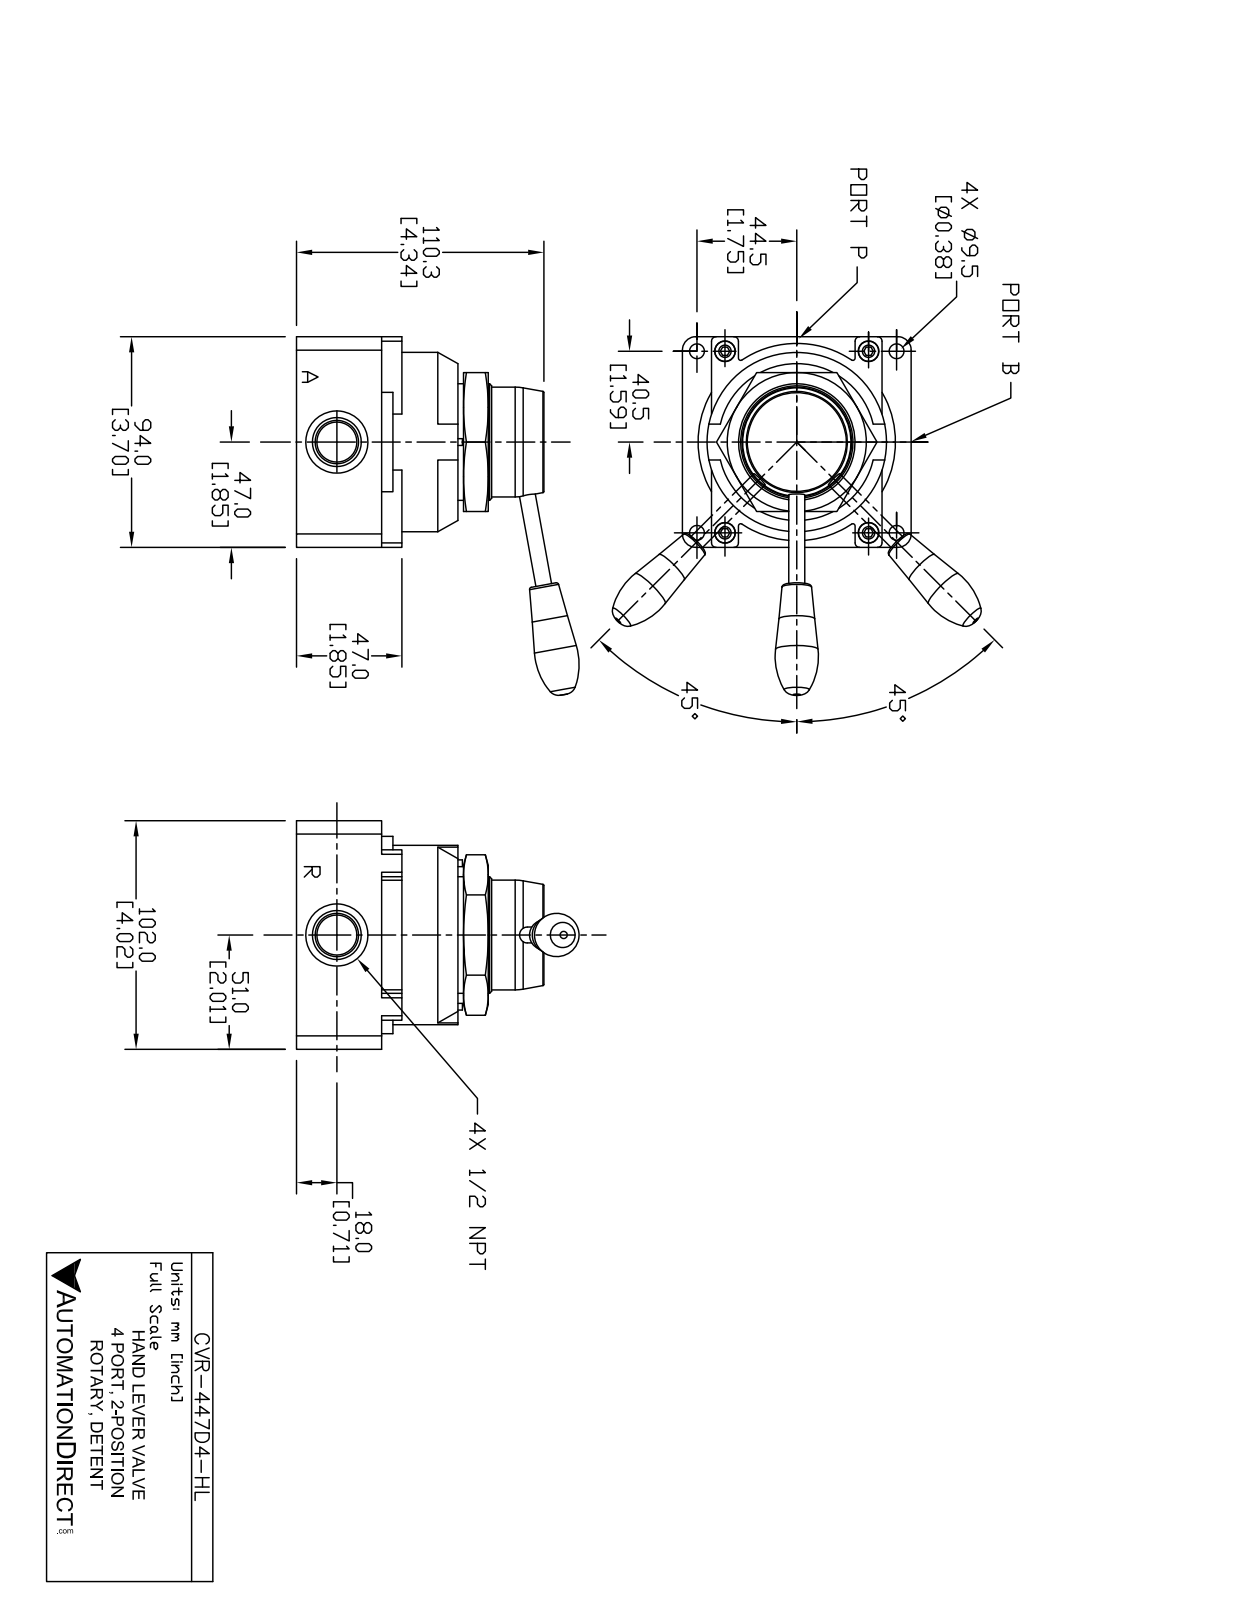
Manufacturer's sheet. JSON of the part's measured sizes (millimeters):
{"part_name": "CVR-447D4-HL", "step_written_by": "SolidWorks 2015 (CONFIG_CONTROL_DESIGN)", "units": "millimeters", "bodies": {"solids": 3, "faces": 221, "planar": 86, "cylindrical": 71, "other": 64}, "overall_size": [160, 126, 102], "volume_mm3": 636600, "surface_area_mm2": 84520, "round_holes": [[6.6, 4], [9.2, 4], [27.7, 2], [26, 1], [44, 1]], "round_bosses_or_shafts": [[9, 4], [3, 2], [80, 1], [52, 1], [49, 1], [26, 1], [7.1, 1]], "partial_cylinders_radius": [[2, 8], [1, 4], [6, 4], [44, 1]], "face_to_face_distances": [94, 102, 87, 43, 44, 29, 72, 15, 110.3, 67.3], "hole_center_spacings": [12.5, 51.6, 60.2, 76.5, 81, 82, 111.4, 64]}
